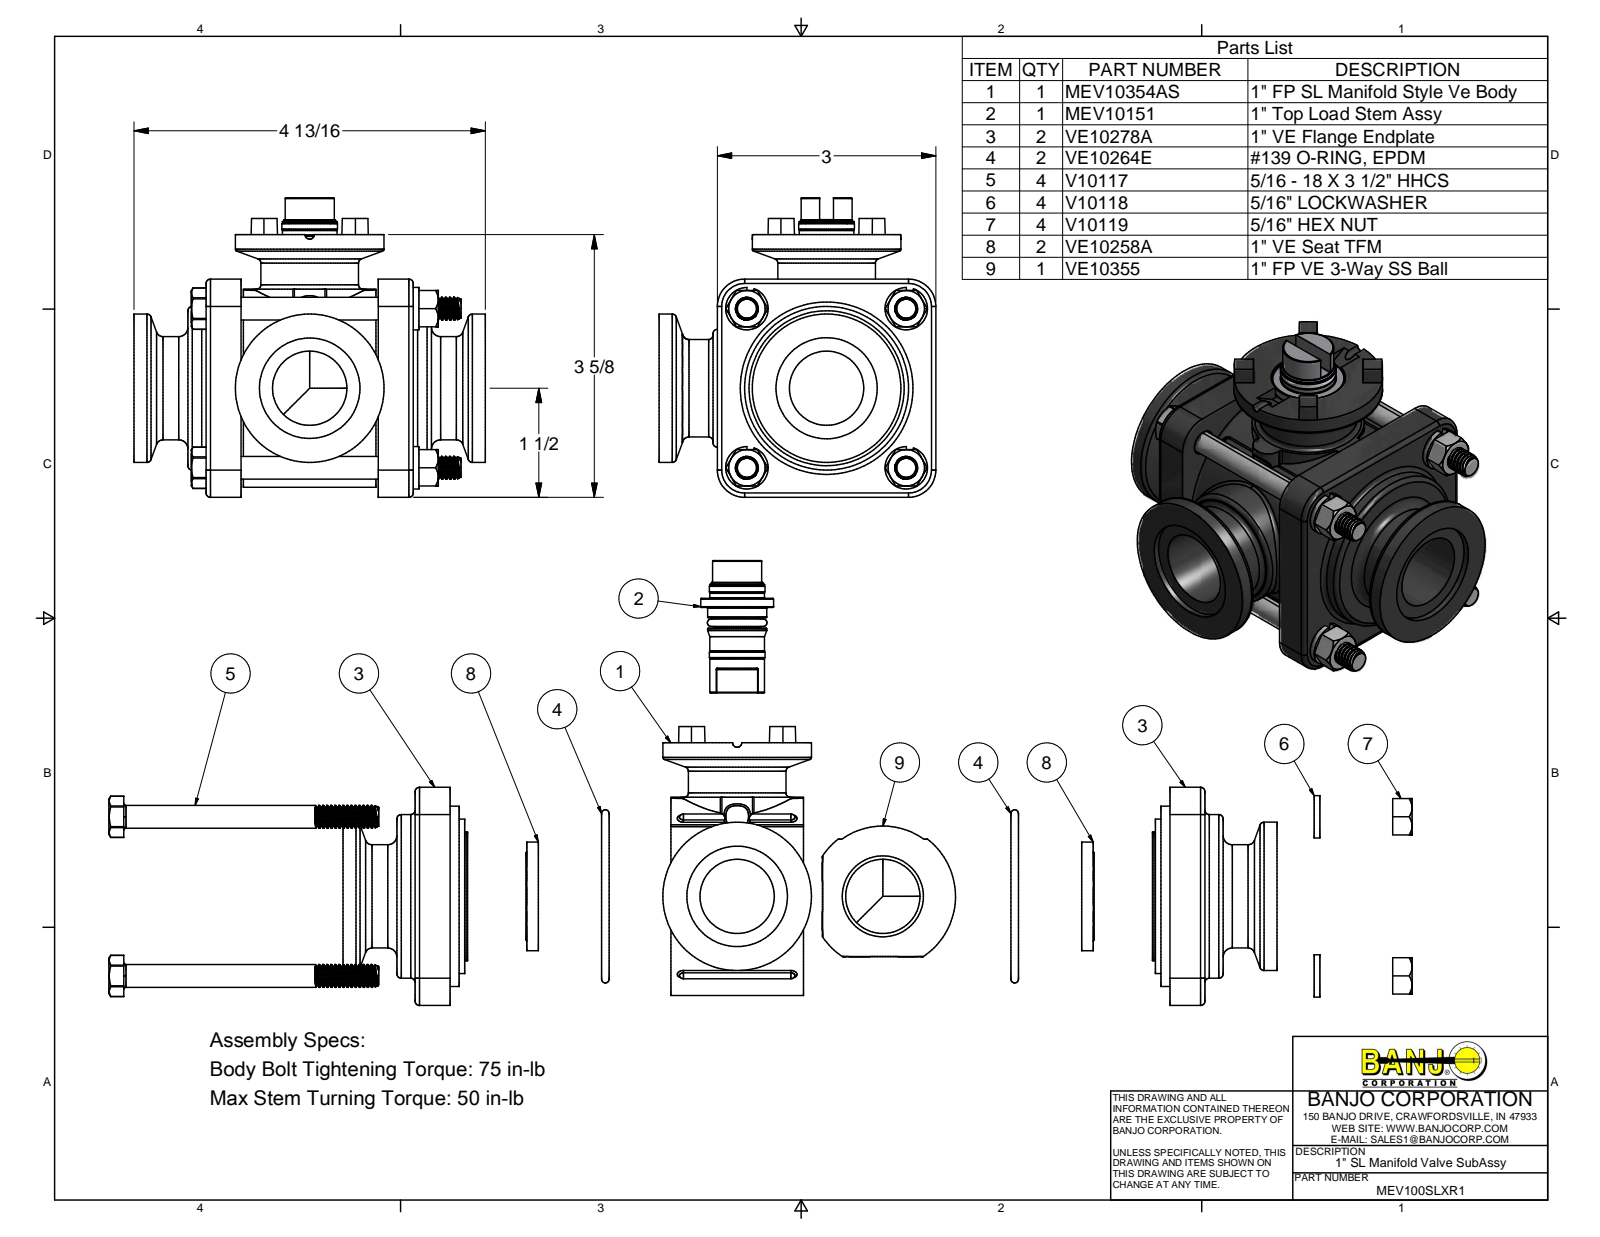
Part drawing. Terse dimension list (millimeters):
name: MEV10354ASX; MEV10354AS; MEV10151SS; FP26041E (+8 more)
written by: Autodesk Inventor 2014 (AUTOMOTIVE_DESIGN)
unit: mm
bodies: 26 solids, 1291 faces (224 planar, 511 cylindrical, 556 other)
size: 122.56 × 104.58 × 96.52
volume: 356 471 mm³; area: 127 208 mm²
holes: 4× ⌀6.41, 4× ⌀8.18, 4× ⌀8.89, 3× ⌀25.91, 1× ⌀16.38, 1× ⌀19.3, 1× ⌀20.78, 1× ⌀35.05, 1× ⌀35.31, 1× ⌀38.1, 1× ⌀53.85, 1× ⌀60.32
bosses: 60× ⌀6.82, 4× ⌀14.81, 4× ⌀7.94, 3× ⌀51.82, 2× ⌀34.04, 1× ⌀69.22, 1× ⌀62.99, 1× ⌀57.15
rounds: 18× R0.76, 12× R1.52, 9× R1.59, 8× R0.25, 8× R3.41, 8× R9.53, 4× R5.33, 4× R7.21
face distances: 12.19, 60.07, 72.26, 76.2, 3.18, 47.88, 25.15, 37.34, 85.22, 97.41
hole spacings: 39.3, 55.58, 78.6
